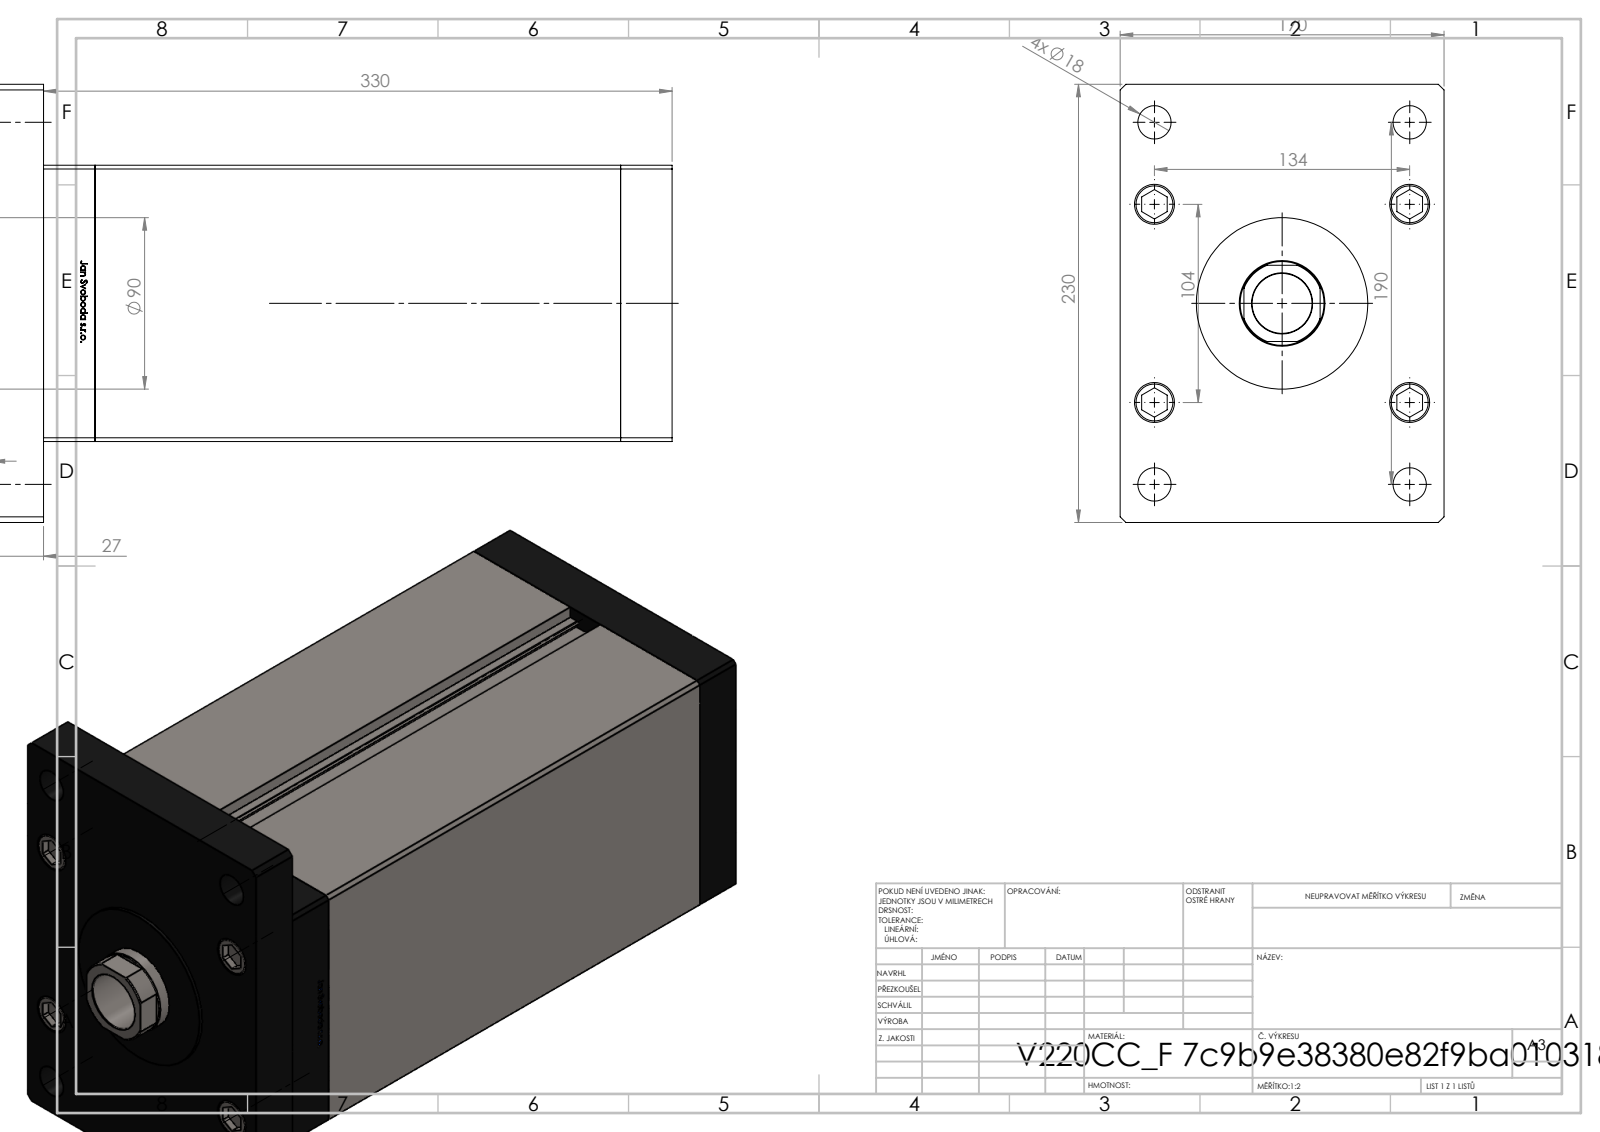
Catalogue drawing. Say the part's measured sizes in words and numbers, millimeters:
The part is named "V220C_F_MIDDLE; V220C BACK_F; V220C_FRONT_F; V220C_F (+2 more)". Its 3-D file was written by "SolidWorks 2019 (CONFIG_CONTROL_DESIGN)". It is 19 solids with 1310 faces: 517 planar, 187 cylindrical and 606 other. Overall it measures 378 by 230 by 170 millimeters. Its volume is 7 686 000 cubic millimeters and its surface area 688 023 square millimeters. Round holes: 9 of diameter 17.5, 5 of diameter 22, 4 of diameter 16, 4 of diameter 21, 2 of diameter 2, 2 of diameter 13.16, 1 of diameter 31.5, 1 of diameter 45, 1 of diameter 46.5. Round bosses or shafts: 9 of diameter 8, 5 of diameter 21, 1 of diameter 100, 1 of diameter 90. Partial cylindrical surfaces (rounded edges, fillets, slot ends): 2 of radius 0.93, 1 of radius 22. The main face-to-face distances are 27, 170, 303, 330, 145, 276, 54, 38, 357, 11. The hole center spacings are 61, 43, 84.81, 116.25, 134, 140.73, 147, 198.91.
